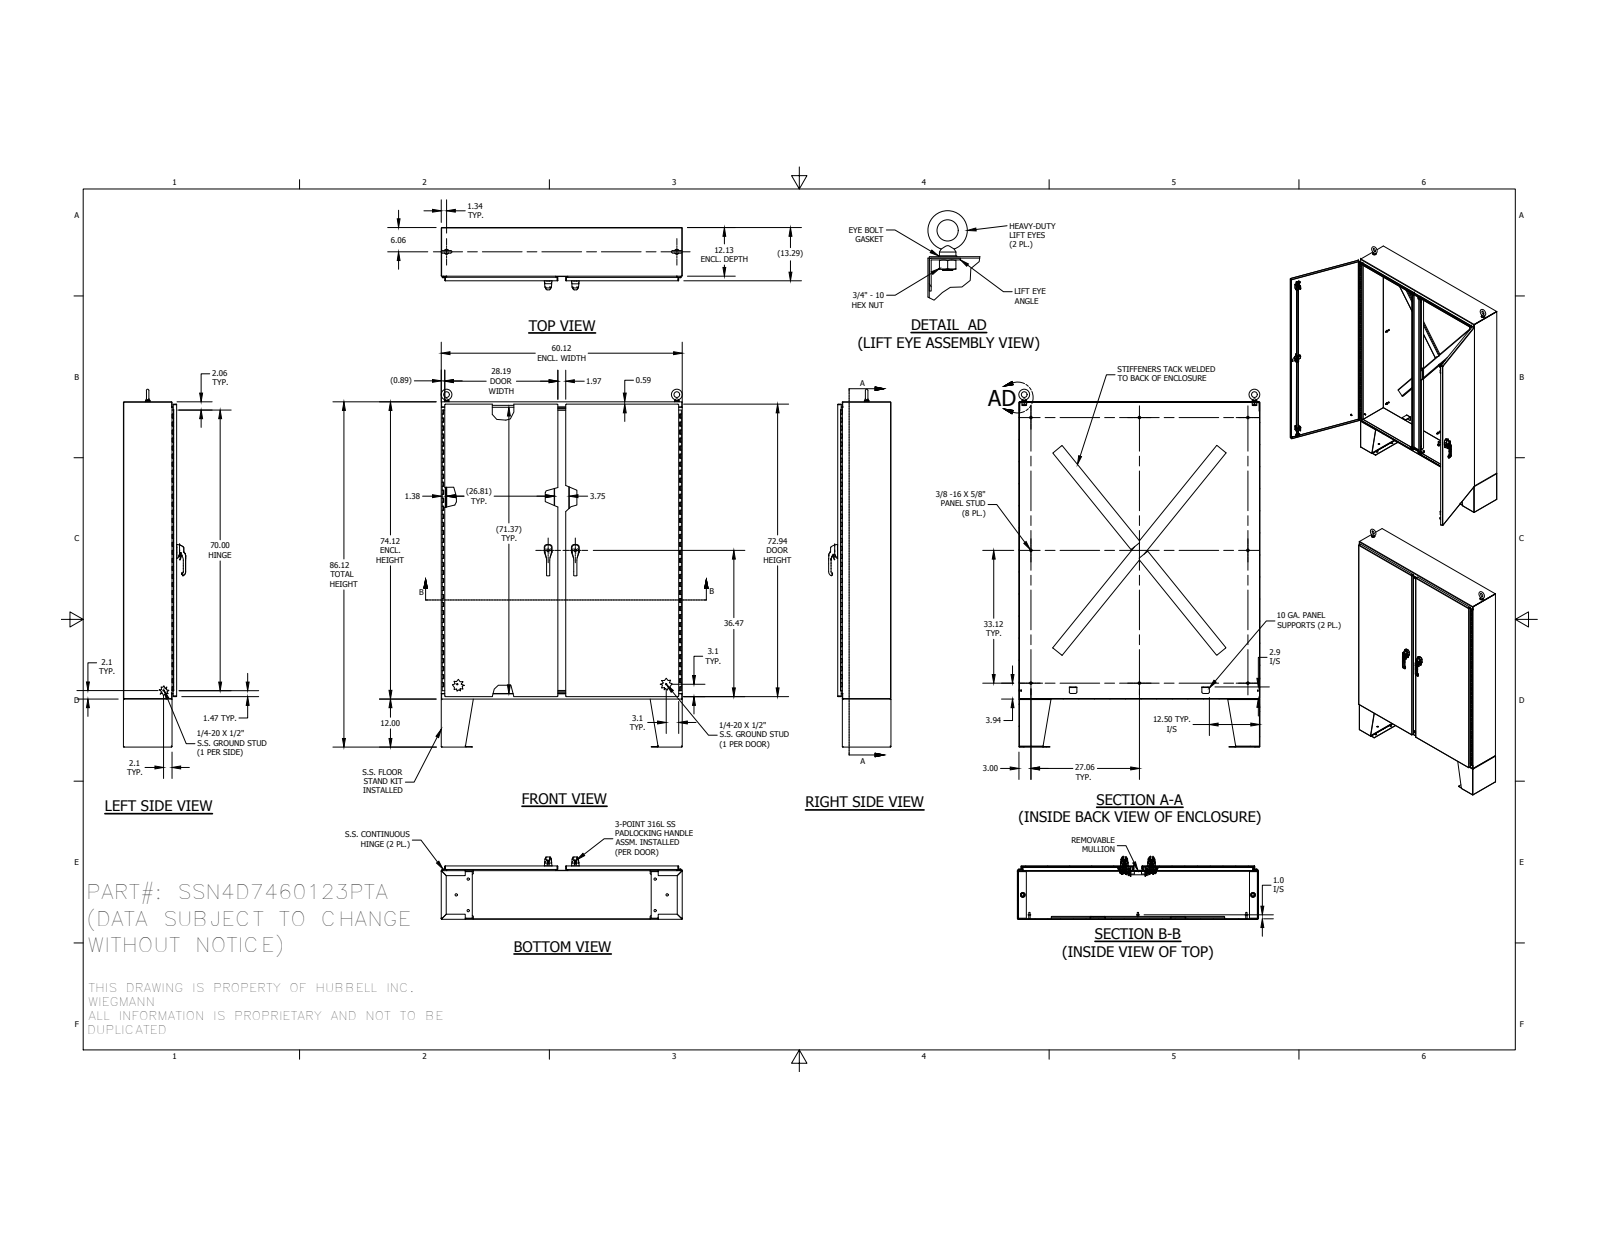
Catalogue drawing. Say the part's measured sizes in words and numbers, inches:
The part is named "38859_1; SSFK1212LG_1; SSN4D743PTRML_1; 349131_1 (+8 more)". Its 3-D file was written by "SolidWorks 2014 (AUTOMOTIVE_DESIGN)". It is 138 solids with 7352 faces: 2804 planar, 2832 cylindrical and 1716 other. Overall it measures 89.248 by 60.125 by 15.538 inches. Its volume is 1 516 cubic inches and its surface area 31 889 square inches. Round holes: 18 of diameter 0.563, 16 of diameter 0.262, 16 of diameter 0.375, 8 of diameter 0.187, 6 of diameter 0.213, 6 of diameter 0.281, 5 of diameter 0.25, 4 of diameter 0.196, 4 of diameter 0.241, 4 of diameter 0.252, 4 of diameter 0.281, 4 of diameter 0.315. Round bosses or shafts: 10 of diameter 0.33, 8 of diameter 0.625, 7 of diameter 0.25, 6 of diameter 0.533, 6 of diameter 0.236, 5 of diameter 1, 4 of diameter 0.563, 4 of diameter 0.531. Partial cylindrical surfaces (rounded edges, fillets, slot ends): 352 of radius 0.02, 213 of radius 0.012, 46 of radius 0.125, 44 of radius 0.019, 34 of radius 0.05, 32 of radius 0.031, 28 of radius 0.079, 24 of radius 0.025. The main face-to-face distances are 0.094, 13.193, 13.196, 13.1, 13.102, 13.287, 0.091, 13.29, 0.096, 60.031. The hole center spacings are 15.556, 0.38, 0.38, 0.76, 7.778, 31.111, 58.326, 64.052.
